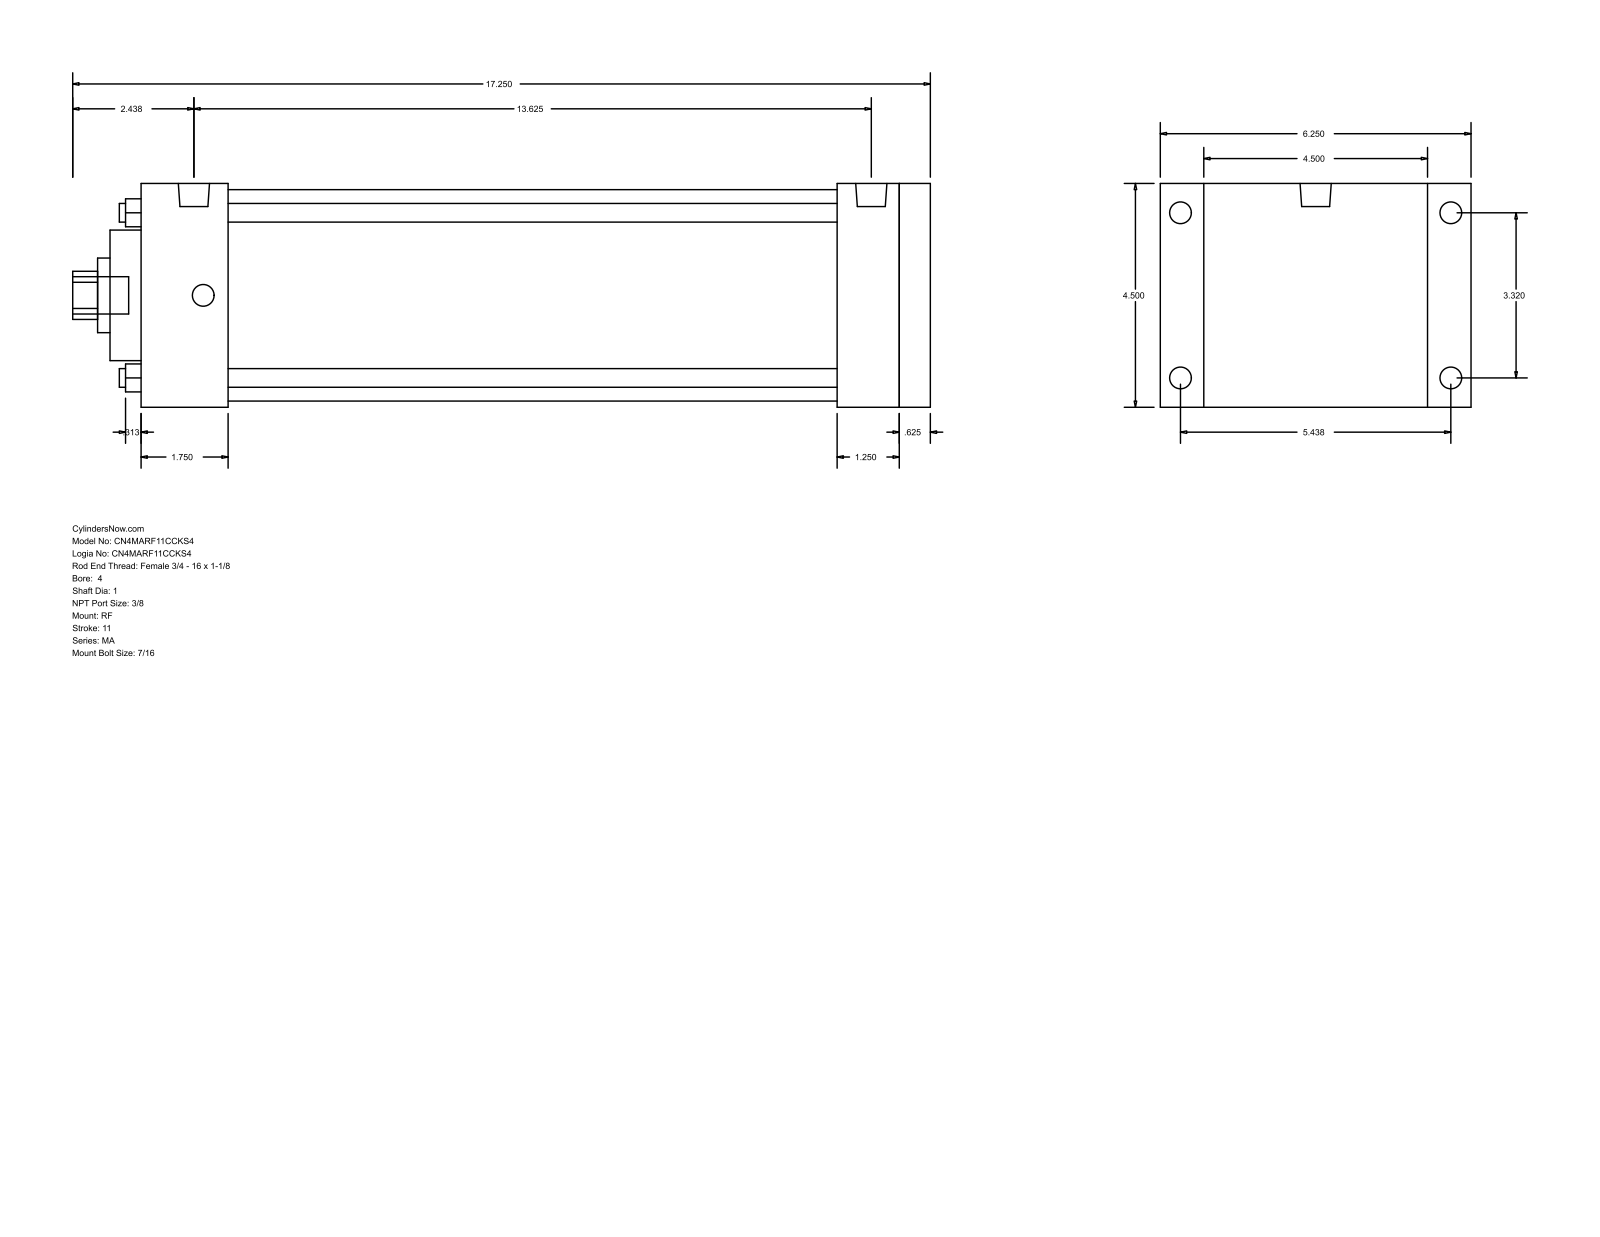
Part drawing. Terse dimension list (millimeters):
name: MA_RF__0400_1
written by: GSSL Pune (CONFIG_CONTROL_DESIGN)
unit: mm
bodies: 0 solids, 94 faces (65 planar, 29 cylindrical, 0 other)
size: 438.15 × 158.75 × 114.3
holes: 4× ⌀9.53, 1× ⌀25.4, 1× ⌀38.1, 1× ⌀66.67, 1× ⌀107.95
bosses: 8× ⌀11.11, 2× ⌀15.93, 1× ⌀19.05
rounds: 1× R12.29
face distances: 114.3, 403.23, 387.35, 15.88, 22.23, 136.53, 355.6, 31.75, 47.63, 44.46
hole spacings: 59.62, 84.32, 119.25
